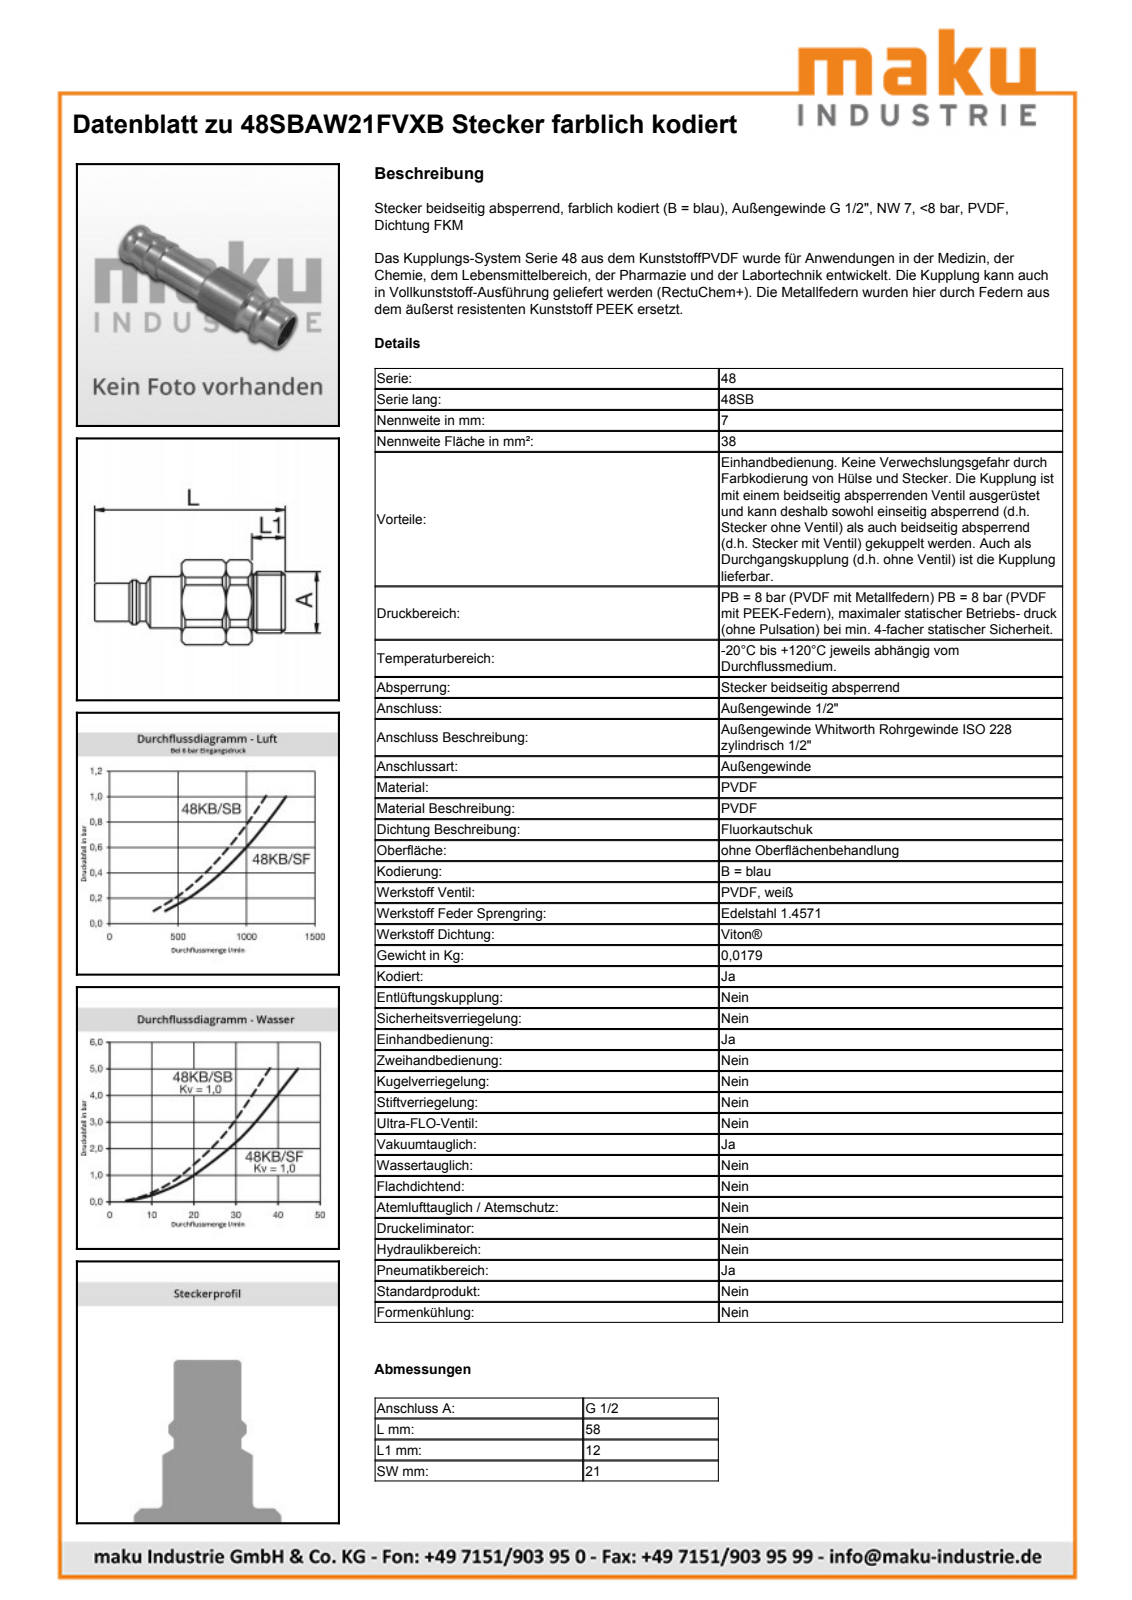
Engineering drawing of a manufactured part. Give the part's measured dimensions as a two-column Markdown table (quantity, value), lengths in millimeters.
| quantity | value |
| --- | --- |
| part name | D107676 |
| STEP written by | Autodesk Inventor 2013 (AUTOMOTIVE_DESIGN) |
| units | millimeters |
| bodies | 1 solid, 71 faces (26 planar, 23 cylindrical, 22 other) |
| overall size | 58 × 25 × 25 |
| volume | 14 925 mm³ |
| surface area | 5 130 mm² |
| round holes (diameter × count) | 16.66 × 1, 18 × 1 |
| round bosses / shafts (diameter × count) | 25 × 1, 20.96 × 1, 13.9 × 1, 13.5 × 1, 12 × 1, 11.79 × 1, 10.3 × 1 |
| partial cylindrical surfaces (radius × count) | 11.5 × 1 |
| main face-to-face distances | 21, 12, 22.5, 10.5, 34.5, 2, 10, 20.5, 32.5, 23.5 |
